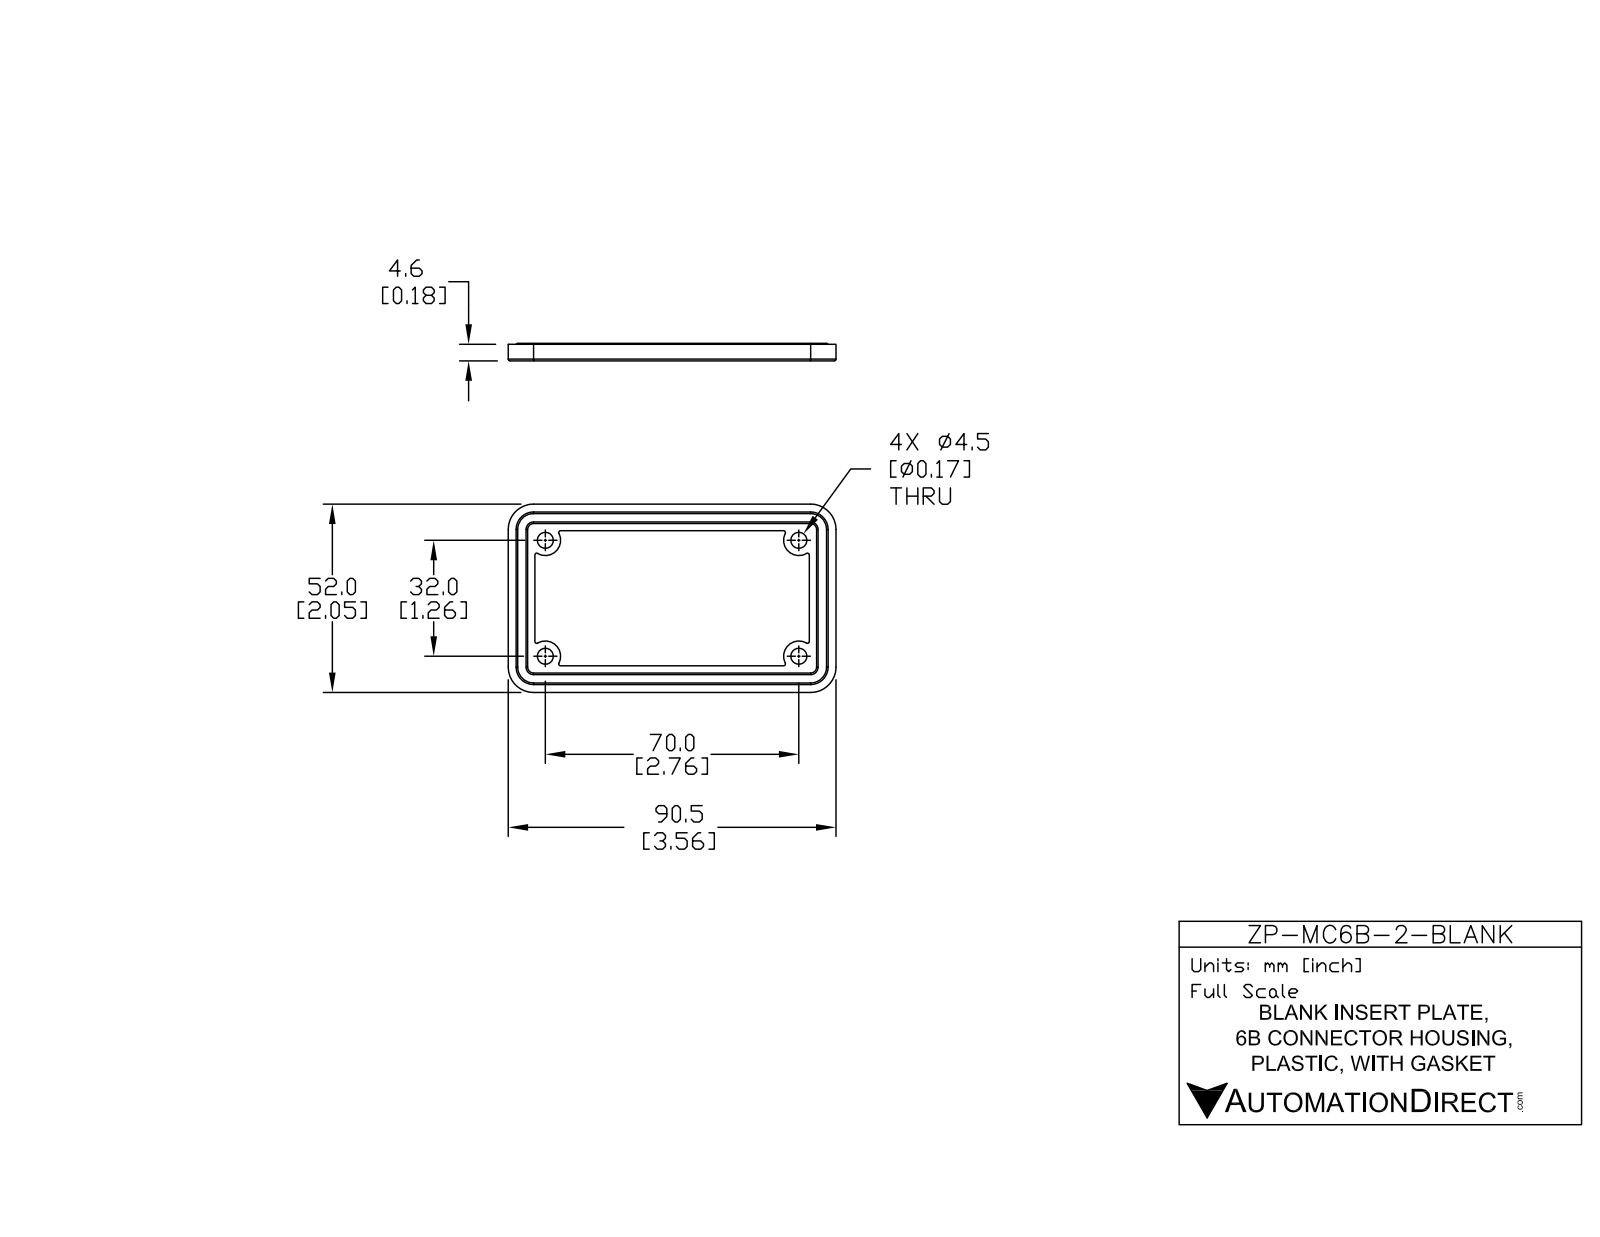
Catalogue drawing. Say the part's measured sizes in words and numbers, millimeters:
The part is named "ZP-MC6B-2-BLANK". Its 3-D file was written by "SolidWorks 2014 (AUTOMOTIVE_DESIGN)". It is 1 solid with 65 faces: 13 planar, 40 cylindrical and 12 other. Overall it measures 90.5 by 52 by 4.85 millimeters. Its volume is 13 386 cubic millimeters and its surface area 11 371 square millimeters. Round holes: 4 of diameter 4.4. Partial cylindrical surfaces (rounded edges, fillets, slot ends): 20 of radius 0.5, 4 of radius 4.2, 4 of radius 7. The main face-to-face distances are 1.6, 3, 4.6, 3.25, 4.85, 7.36, 44.64, 52, 37.28, 90.5. The hole center spacings are 32, 70, 76.97.
